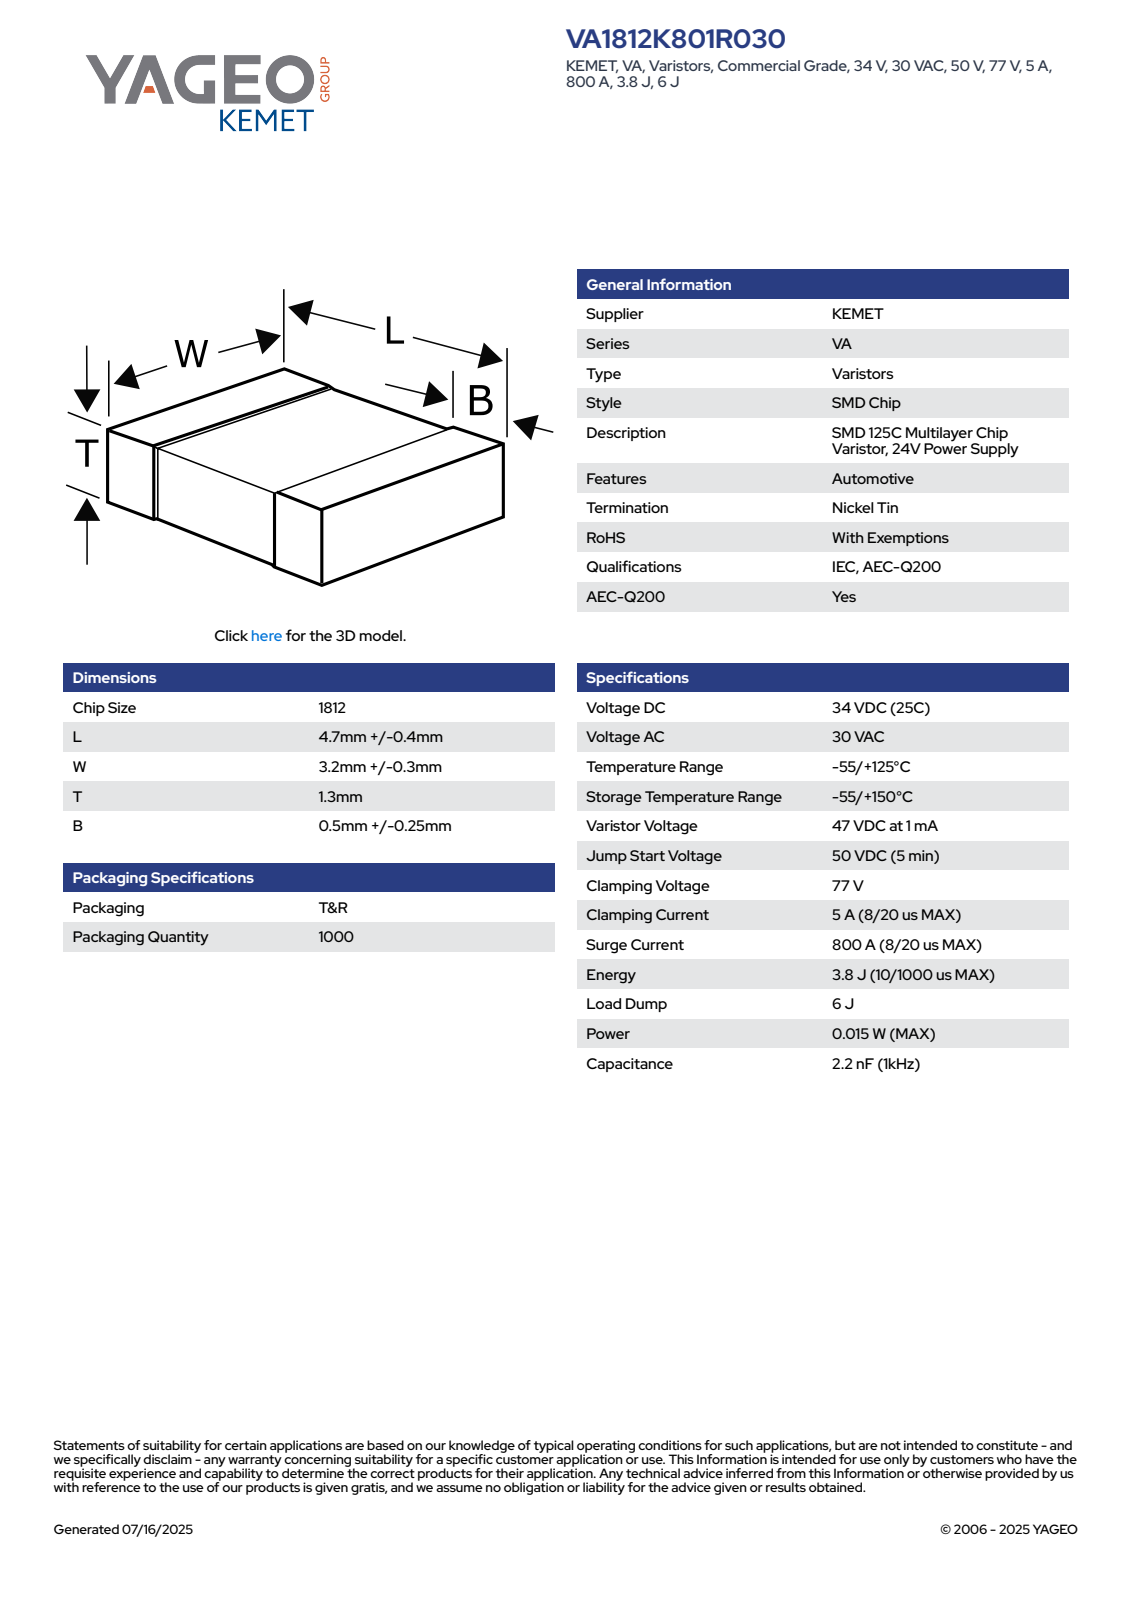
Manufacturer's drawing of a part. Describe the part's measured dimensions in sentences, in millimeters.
The part is named "VS_SMD_1812_L5.10W3.5T1.3B0.75". Its 3-D file was written by "SolidWorks 2014 (AUTOMOTIVE_DESIGN)". It is 4 solids with 125 faces: 71 planar, 38 cylindrical and 16 other. Overall it measures 5.1 by 3.5 by 1.3 millimeters. Its volume is 21 cubic millimeters and its surface area 57 square millimeters. The main face-to-face distances are 1.16, 1.23, 1.3, 5.1, 3.36, 3.43, 3.5, 2.24, 2.86, 2.75.
